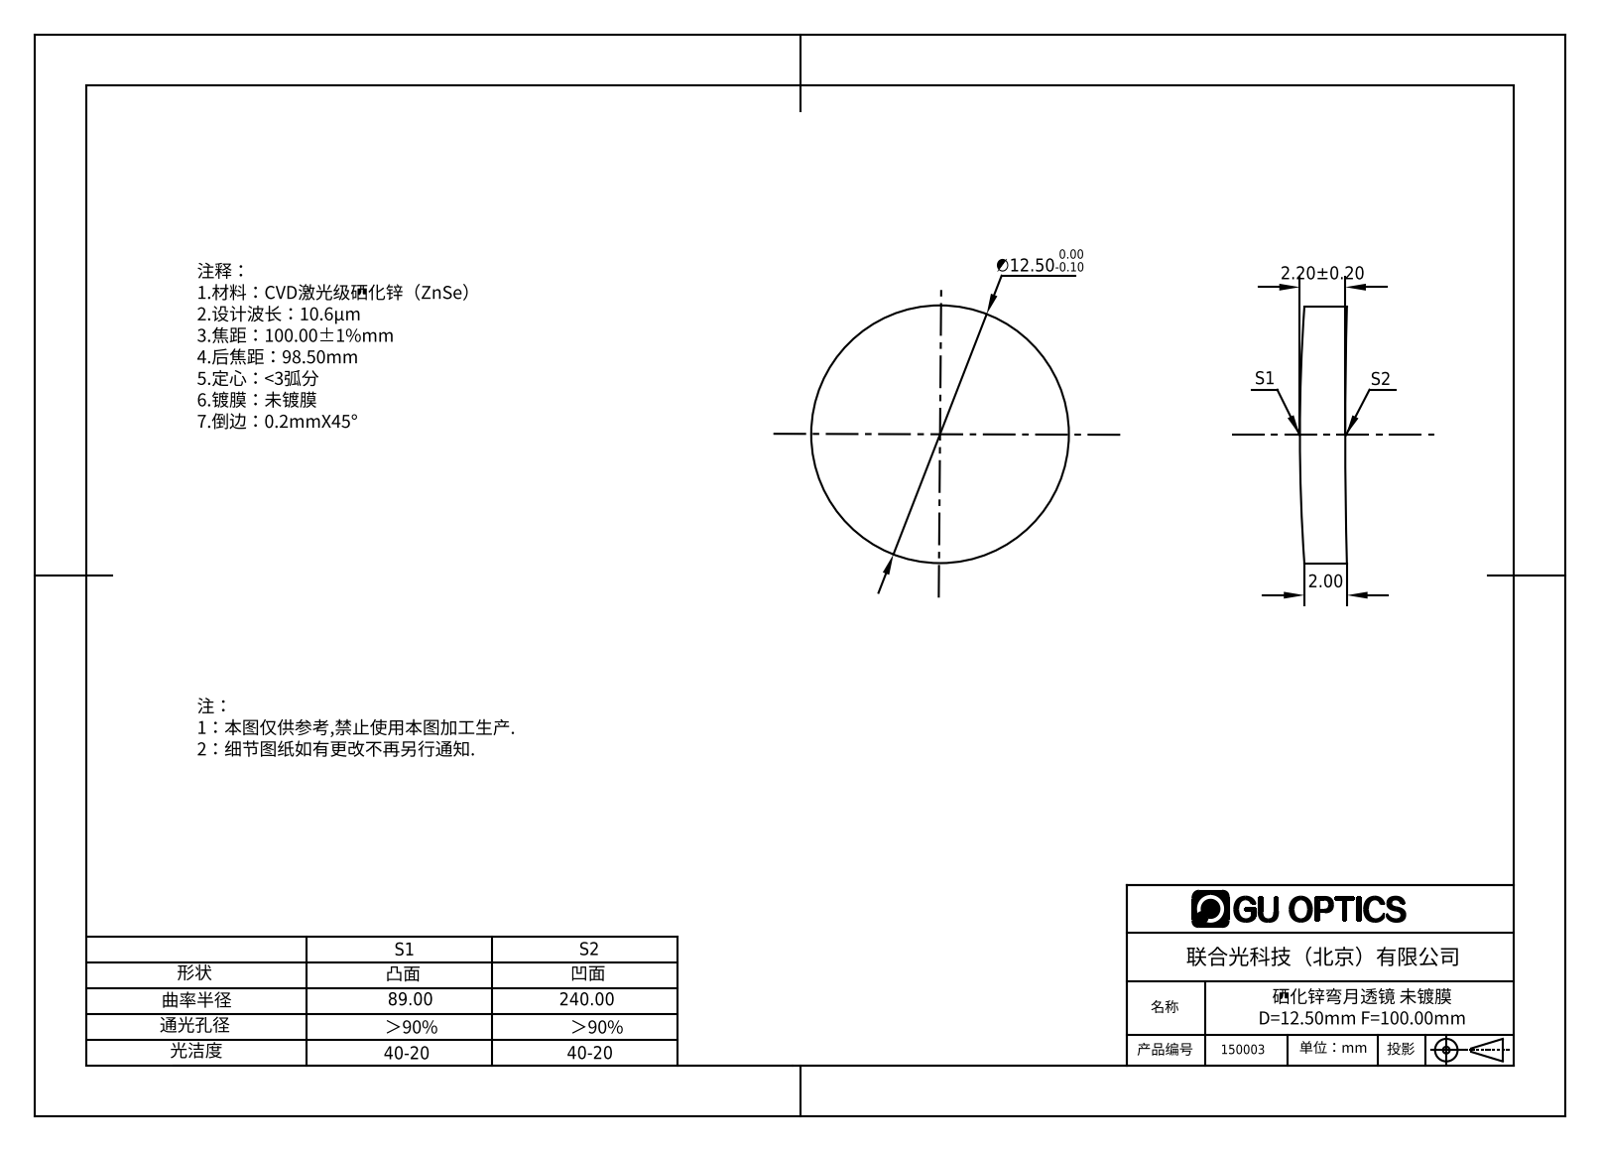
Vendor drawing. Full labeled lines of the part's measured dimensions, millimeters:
Part name (STEP PRODUCT): 150003
STEP written by: SolidWorks 2016 (AUTOMOTIVE_DESIGN)
Units: millimetres
Bodies: 1 solid, 6 faces (0 planar, 2 cylindrical, 4 other)
Overall size (bounding box): 12.5 × 12.5 × 2.28
Volume: 261 mm³ · Surface area: 327 mm²
Round bosses / shafts (diameter × count): ⌀12.5 ×1
